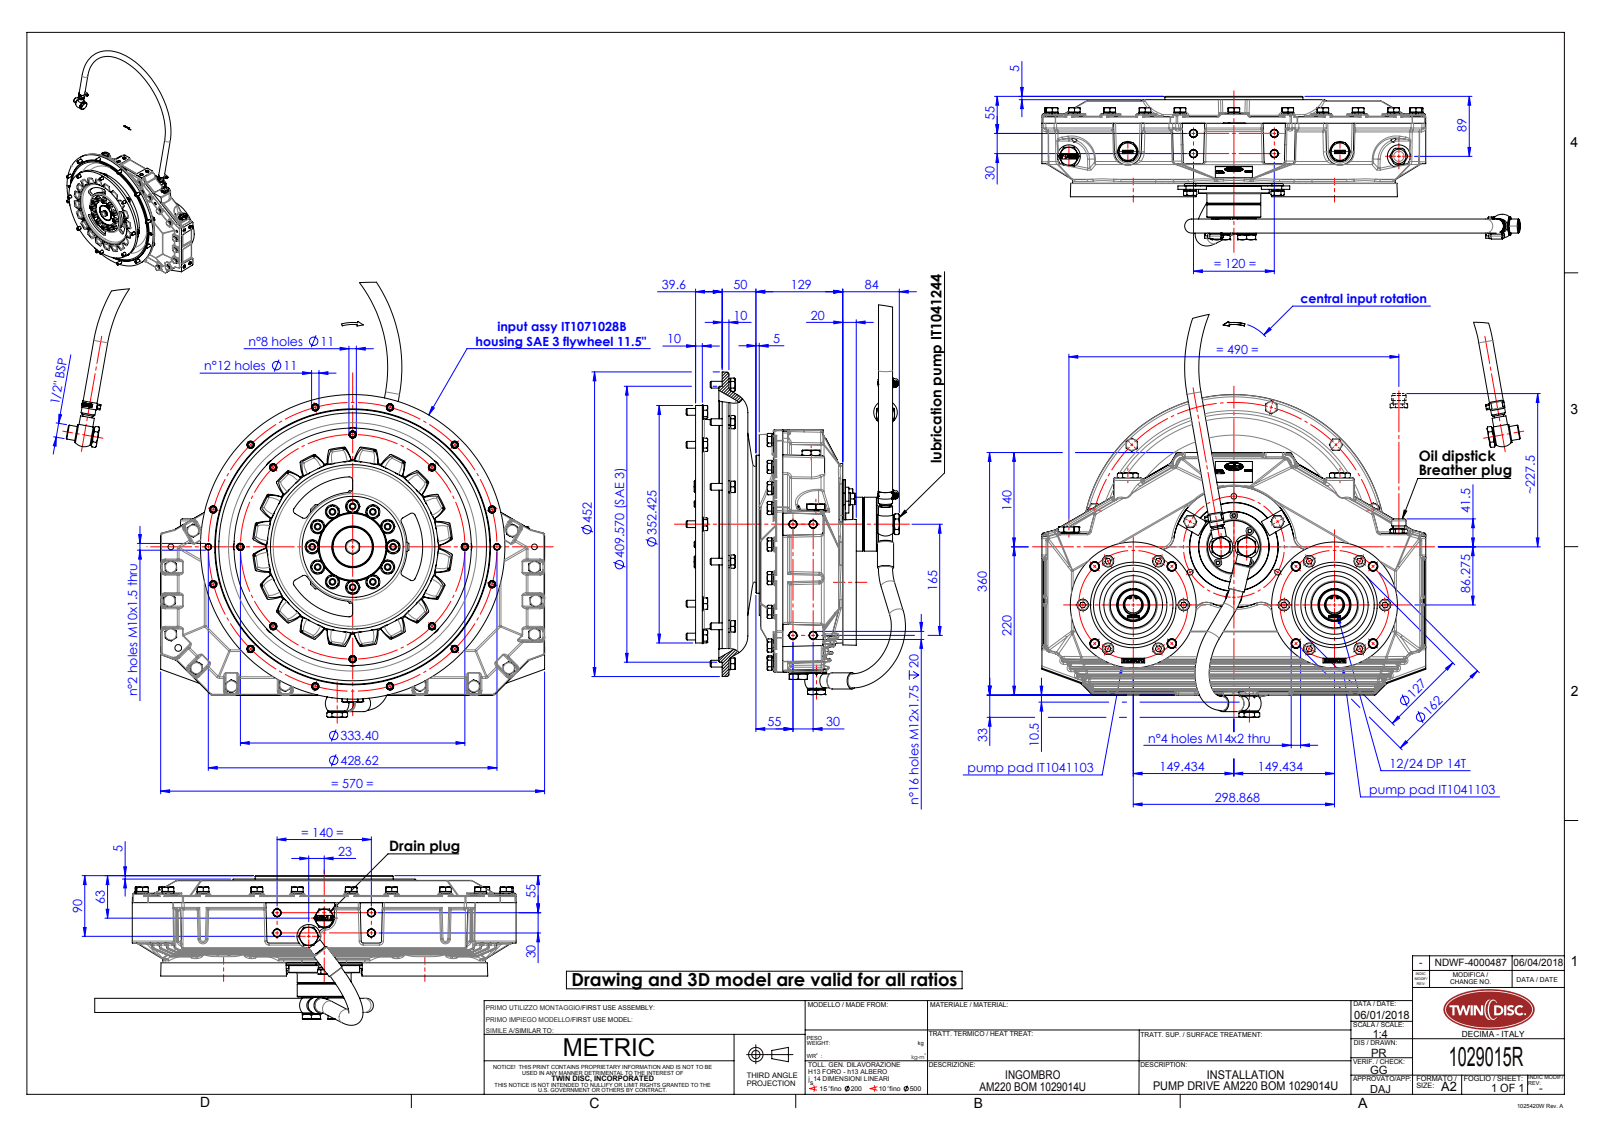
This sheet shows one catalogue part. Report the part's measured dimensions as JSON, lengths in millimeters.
{"part_name": "1029015R; IT1041244_A-installation; IT1071028B_rev02-installation; IT1041103_rev00-installation (+5 more)", "step_written_by": "SolidWorks 2015 (AUTOMOTIVE_DESIGN)", "units": "millimeters", "bodies": {"solids": 202, "faces": 9116, "planar": 4085, "cylindrical": 2374, "other": 2657}, "overall_size": [749.88, 710.43, 325.71], "volume_mm3": 21040000, "surface_area_mm2": 3016000, "round_holes": [[10.5, 69], [8.5, 52], [10.2, 46], [11, 33], [12, 26], [17, 12], [13, 11], [21, 11], [8, 10], [14, 8], [5, 6], [7, 6]], "round_bosses_or_shafts": [[10, 85], [16.2, 65], [18.1, 45], [21, 25], [16, 12], [27, 7], [6, 6], [18, 5]], "partial_cylinders_radius": [[2, 188], [5, 169], [3, 166], [1, 103], [4, 80], [2.5, 55], [42.91, 40], [1.5, 30]], "face_to_face_distances": [149, 20, 60, 10, 89, 38.5, 110.5, 11.5, 40, 169], "hole_center_spacings": [57.4, 120, 138.58, 30, 207.84, 210.17, 10, 31.62]}
